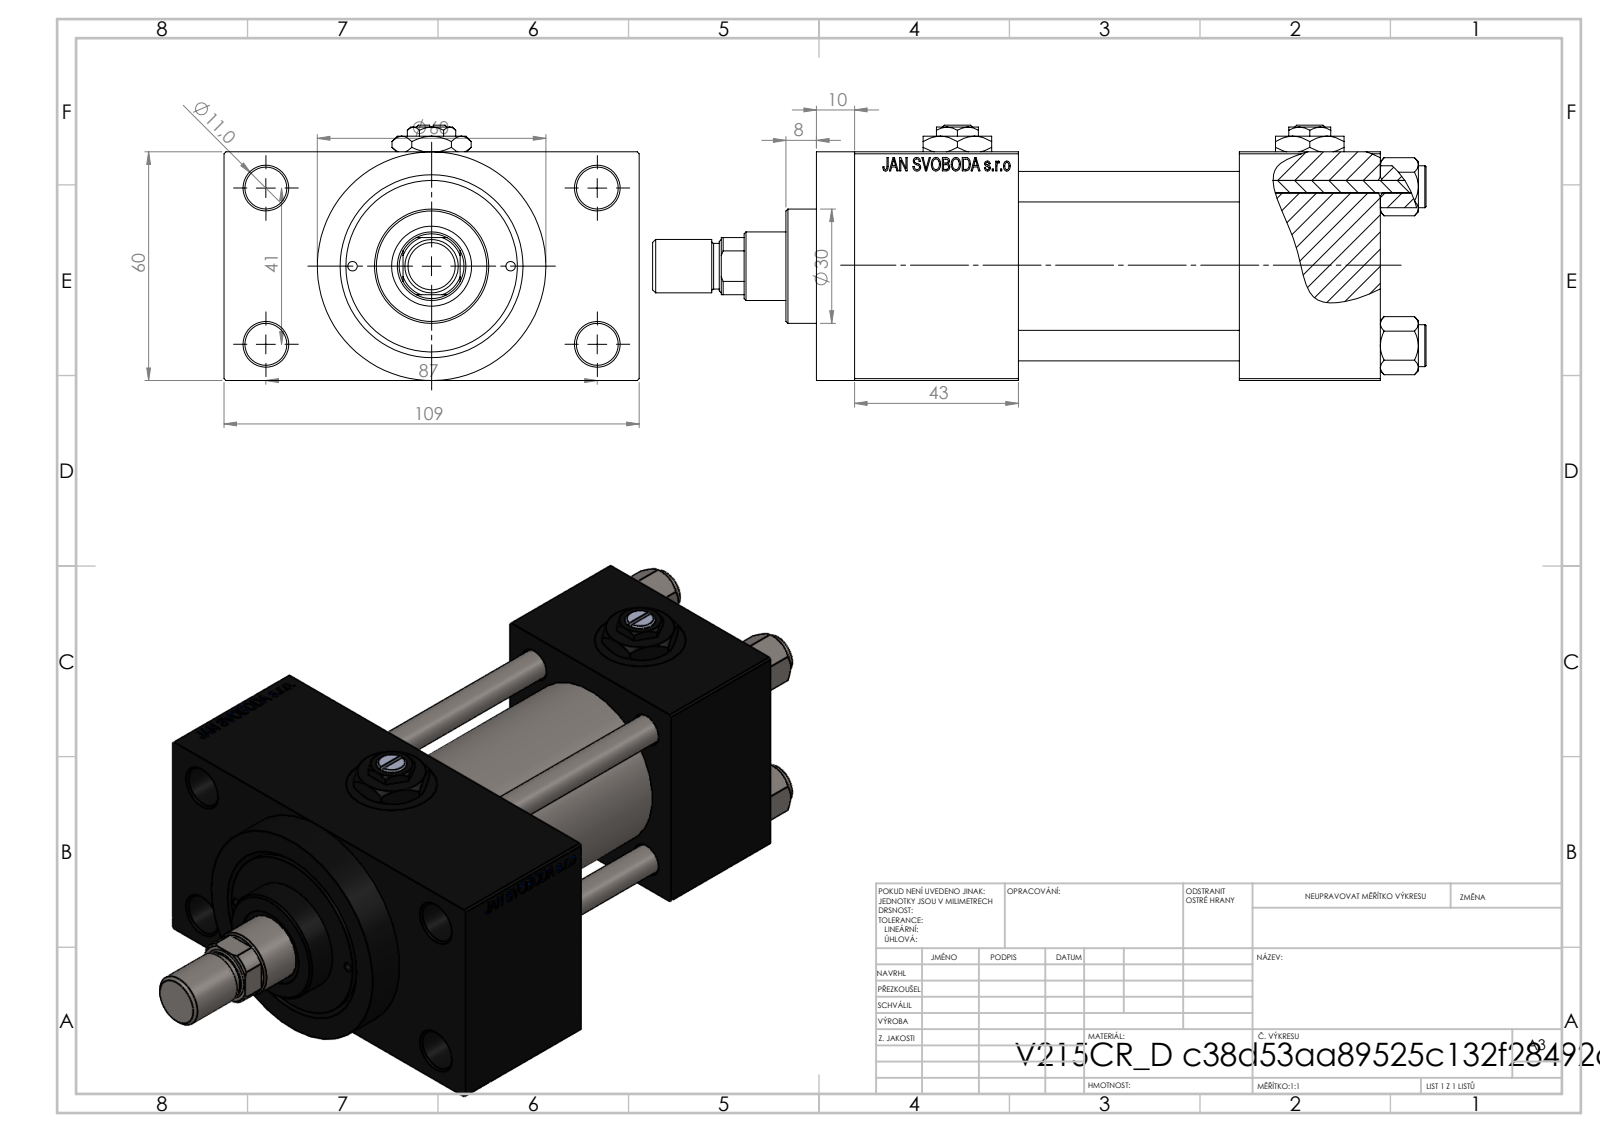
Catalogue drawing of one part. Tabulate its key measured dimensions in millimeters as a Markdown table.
| quantity | value |
| --- | --- |
| part name | ROD_END_AH; V215CR_D_TYCINKA; Zatka_pro_OIL_PORT; V215CR_VCP_D (+3 more) |
| STEP written by | SolidWorks 2019 (CONFIG_CONTROL_DESIGN) |
| units | millimeters |
| bodies | 14 solids, 1228 faces (552 planar, 108 cylindrical, 568 other) |
| overall size | 203 × 109 × 67 |
| volume | 518 053 mm³ |
| surface area | 124 998 mm² |
| round holes (diameter × count) | 8 × 4, 11 × 4, 2.5 × 2, 7 × 2, 16.66 × 2, 24 × 2, 8.5 × 1, 18 × 1, 21 × 1, 31 × 1, 40 × 1, 45 × 1 |
| round bosses / shafts (diameter × count) | 11 × 4, 60 × 1, 46 × 1, 30 × 1, 14 × 1, 12 × 1 |
| partial cylindrical surfaces (radius × count) | 8.5 × 1 |
| main face-to-face distances | 60, 24.5, 84.5, 58, 37, 95, 43, 138, 101, 109 |
| hole center spacings | 20.85, 22.65, 29.49, 30.62, 41.7, 46.53, 47.15, 48.09 |
